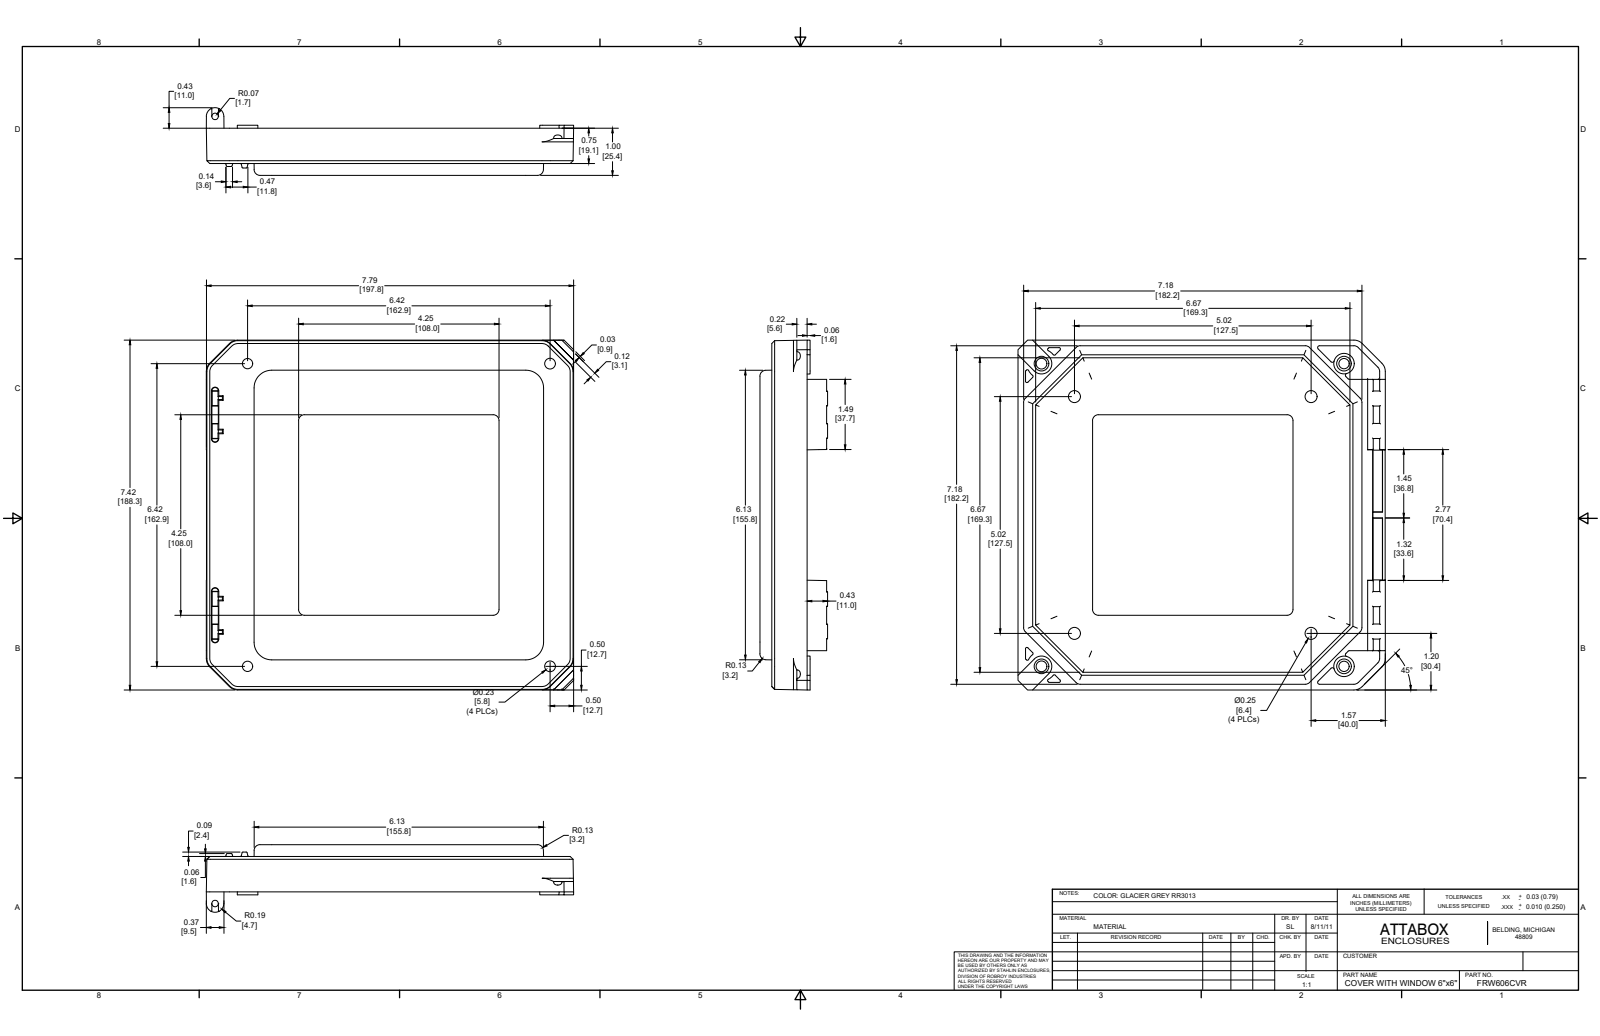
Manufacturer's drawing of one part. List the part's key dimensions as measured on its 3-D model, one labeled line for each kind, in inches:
Part name (STEP PRODUCT): FRW606CVR
STEP written by: SolidWorks 2019 (AUTOMOTIVE_DESIGN)
Units: inches
Bodies: 1 solid, 581 faces (237 planar, 196 cylindrical, 148 other)
Overall size (bounding box): 7.79 × 7.415 × 1.434
Volume: 13.91 in³ · Surface area: 150 in²
Round holes (diameter × count): ⌀0.253 ×4, ⌀0.219 ×2, ⌀0.227 ×2, ⌀0.313 ×2, ⌀0.137 ×1
Round bosses / shafts (diameter × count): ⌀0.435 ×2
Partial cylindrical surfaces — rounded edges, fillets, slot ends (radius × count): R0.03 ×23, R0.096 ×16, R0.125 ×16, R0.01 ×14, R0.062 ×12, R0.063 ×12, R0.04 ×10, R0.06 ×9
Main face-to-face distances: 0.25, 0.125, 0.125, 0.375, 0.75, 1, 0.875, 0.625, 0.375, 0.625
Hole centre spacings: 5.759, 6.415, 0.987, 0.988, 5.018, 5.018, 5.758, 5.759
